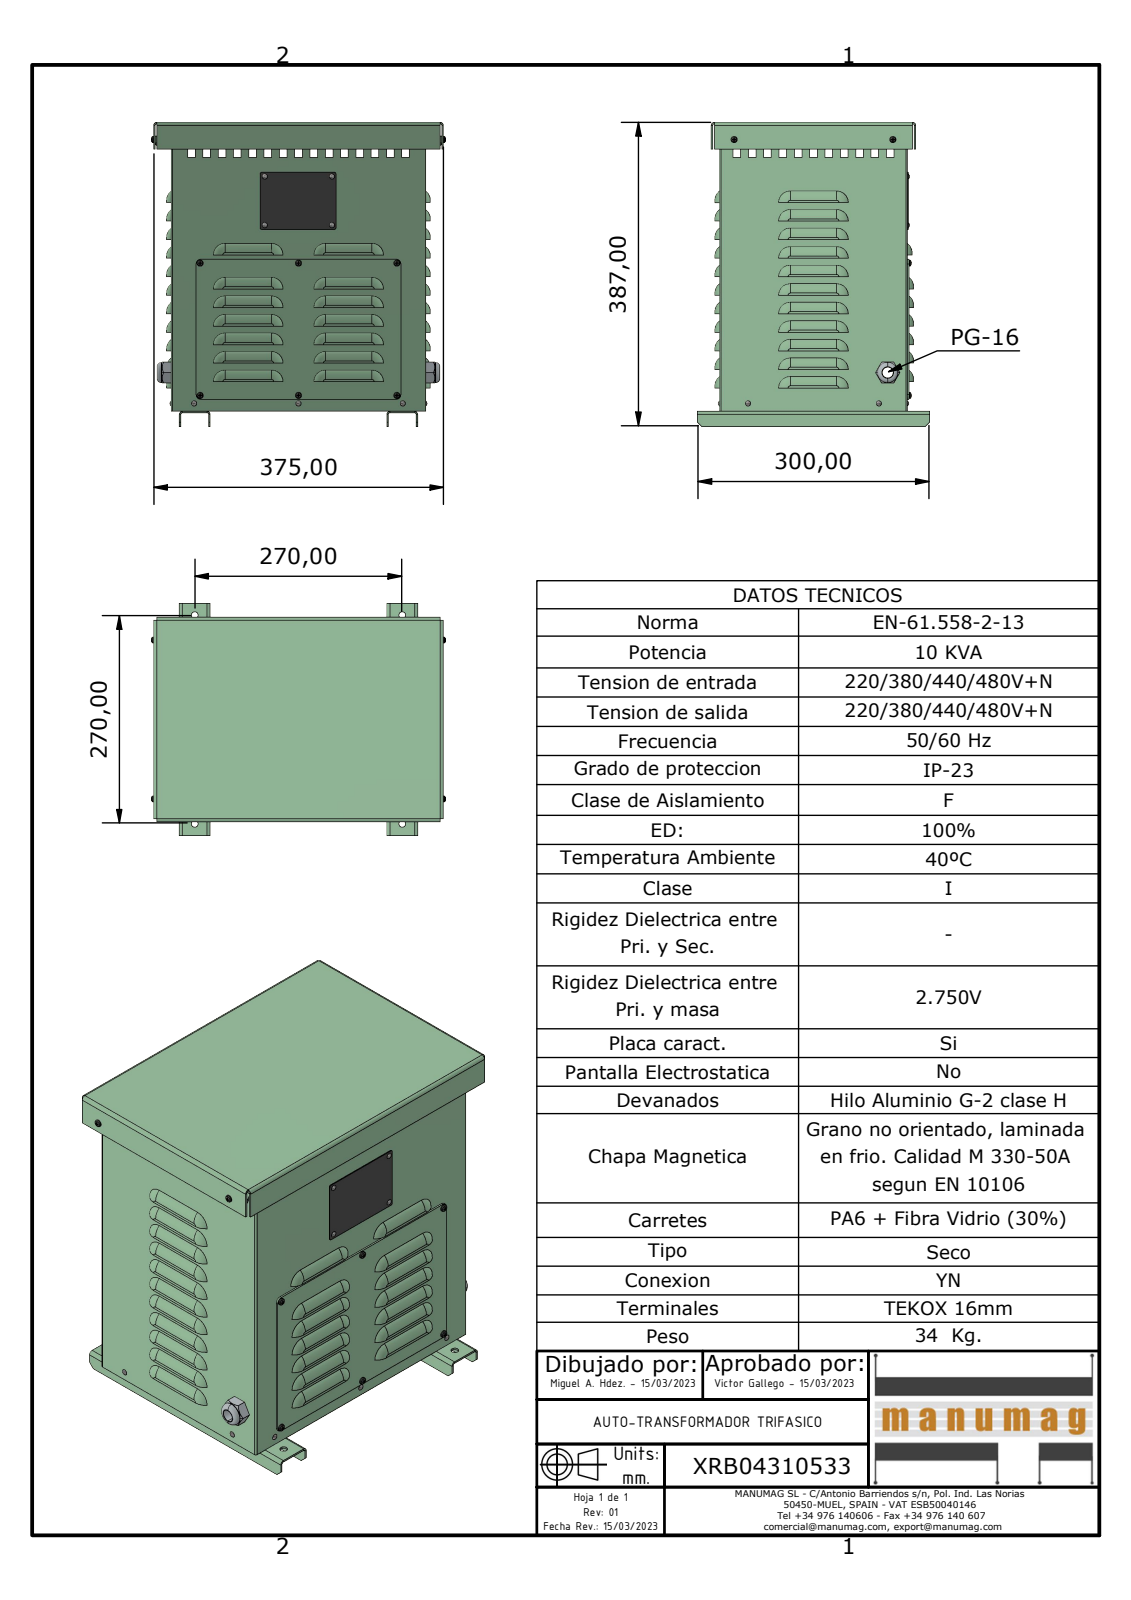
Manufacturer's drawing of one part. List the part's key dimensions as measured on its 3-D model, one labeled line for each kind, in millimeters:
Part name (STEP PRODUCT): XRB04310533; JE010 EXPORT BASE; JE010 EXPORT PATA; JE010 EXPORT CUERPO (+6 more)
STEP written by: Autodesk Inventor 2023 (AUTOMOTIVE_DESIGN)
Units: millimetres
Bodies: 33 solids, 1975 faces (1082 planar, 421 cylindrical, 472 other)
Overall size (bounding box): 394.02 × 381.14 × 300
Volume: 1 720 000 mm³ · Surface area: 1 517 000 mm²
Round holes (diameter × count): ⌀2.3 ×8, ⌀3.7 ×8, ⌀8.8 ×8, ⌀4.3 ×5, ⌀3.4 ×4, ⌀4 ×4, ⌀5 ×3, ⌀14 ×1, ⌀24 ×1
Round bosses / shafts (diameter × count): ⌀3.2 ×9, ⌀4 ×8, ⌀3.62 ×8, ⌀26 ×1, ⌀23 ×1, ⌀22.5 ×1
Partial cylindrical surfaces — rounded edges, fillets, slot ends (radius × count): R14 ×105, R4 ×68, R15 ×40, R2 ×20, R1.5 ×6, R2 ×5, R6 ×4
Main face-to-face distances: 2, 240.62, 327.32, 372.01, 242.62, 374.01, 238.62, 325.32, 329.32, 4
Hole centre spacings: 55.99, 127.3, 168.89, 210.03, 213.21, 213.3, 342.86, 62.98
